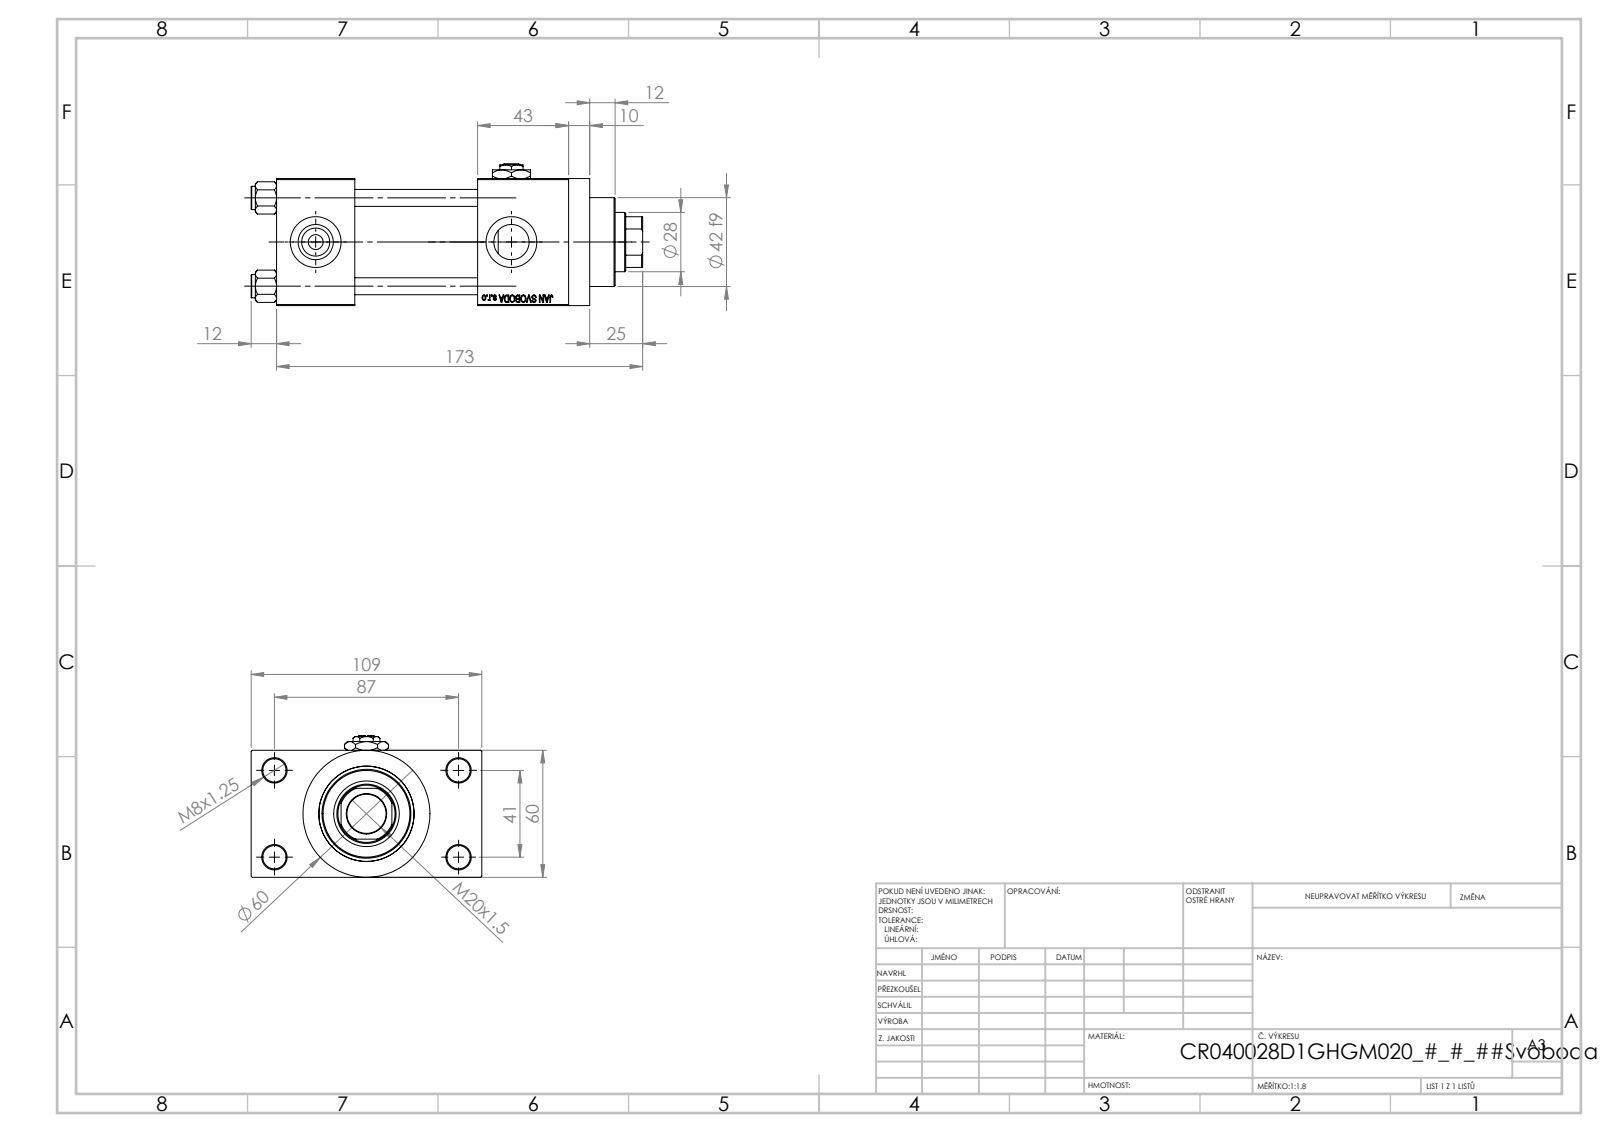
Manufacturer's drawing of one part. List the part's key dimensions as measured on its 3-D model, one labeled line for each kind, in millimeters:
Part name (STEP PRODUCT): V215_VC_A; NUT_M5_D; V215CR_D_Body; V215CR_D_TYCINKA (+2 more)
STEP written by: SolidWorks 2019 (CONFIG_CONTROL_DESIGN)
Units: millimetres
Bodies: 12 solids, 1152 faces (522 planar, 92 cylindrical, 538 other)
Overall size (bounding box): 185 × 109 × 67
Volume: 528 443 mm³ · Surface area: 130 018 mm²
Round holes (diameter × count): ⌀8 ×4, ⌀11 ×4, ⌀16.66 ×3, ⌀24 ×3, ⌀7 ×2, ⌀18.5 ×1, ⌀28 ×1, ⌀31 ×1, ⌀40 ×1, ⌀45 ×1
Round bosses / shafts (diameter × count): ⌀11 ×4, ⌀60 ×1, ⌀46 ×1, ⌀42 ×1
Partial cylindrical surfaces — rounded edges, fillets, slot ends (radius × count): R13.5 ×1
Main face-to-face distances: 60, 58, 24.5, 84.5, 37, 95, 138, 101, 43, 109
Hole centre spacings: 22.65, 29.49, 41.7, 47.15, 48.09, 64.35, 76.49, 41
